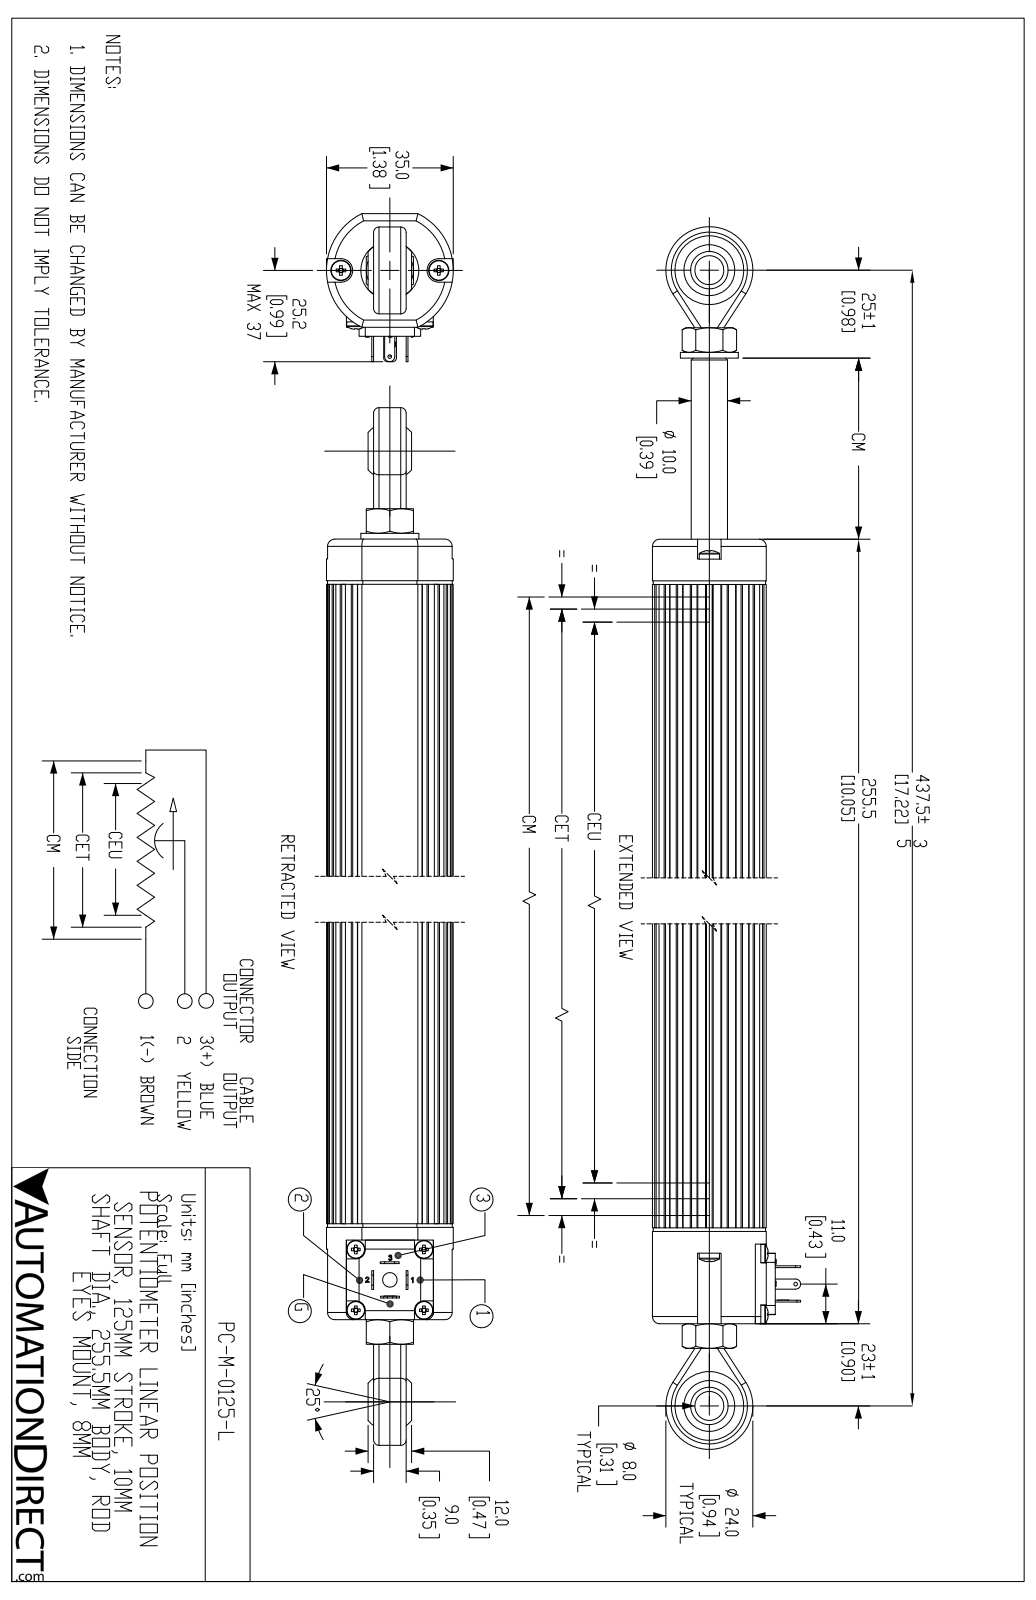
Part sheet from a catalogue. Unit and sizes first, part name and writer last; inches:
Units: inches
Overall size (bounding box): 13.095 × 1.61 × 1.378
Round holes (diameter × count): ⌀0.087 ×4, ⌀0.102 ×4, ⌀0.039 ×3, ⌀0.108 ×2, ⌀0.138 ×2, ⌀0.315 ×2, ⌀0.748 ×2, ⌀0.114 ×1, ⌀0.157 ×1, ⌀0.268 ×1, ⌀0.331 ×1, ⌀0.512 ×1
Round bosses / shafts (diameter × count): ⌀0.197 ×4, ⌀0.098 ×4, ⌀0.118 ×3, ⌀0.22 ×2, ⌀0.63 ×1, ⌀0.394 ×1, ⌀0.39 ×1, ⌀0.315 ×1
Partial cylindrical surfaces — rounded edges, fillets, slot ends (radius × count): R0.059 ×8, R0.039 ×5, R0.079 ×5, R0.102 ×4, R0.118 ×4, R0.055 ×2, R0.128 ×2, R0.472 ×2
Main face-to-face distances: 1.236, 0.039, 8.563, 8.524, 8.602, 0.118, 1.118, 0.913, 9.606, 1.004
Hole centre spacings: 0.496, 0.531, 0.661, 0.74, 0.993, 0.024, 0.11, 0.134
Volume: 15.9 in³ · Surface area: 95.95 in²
Bodies: 26 solids, 1441 faces (437 planar, 366 cylindrical, 638 other)
Part name (STEP PRODUCT): PC-M-0125-L
STEP written by: SolidWorks 2019 (AUTOMOTIVE_DESIGN)
